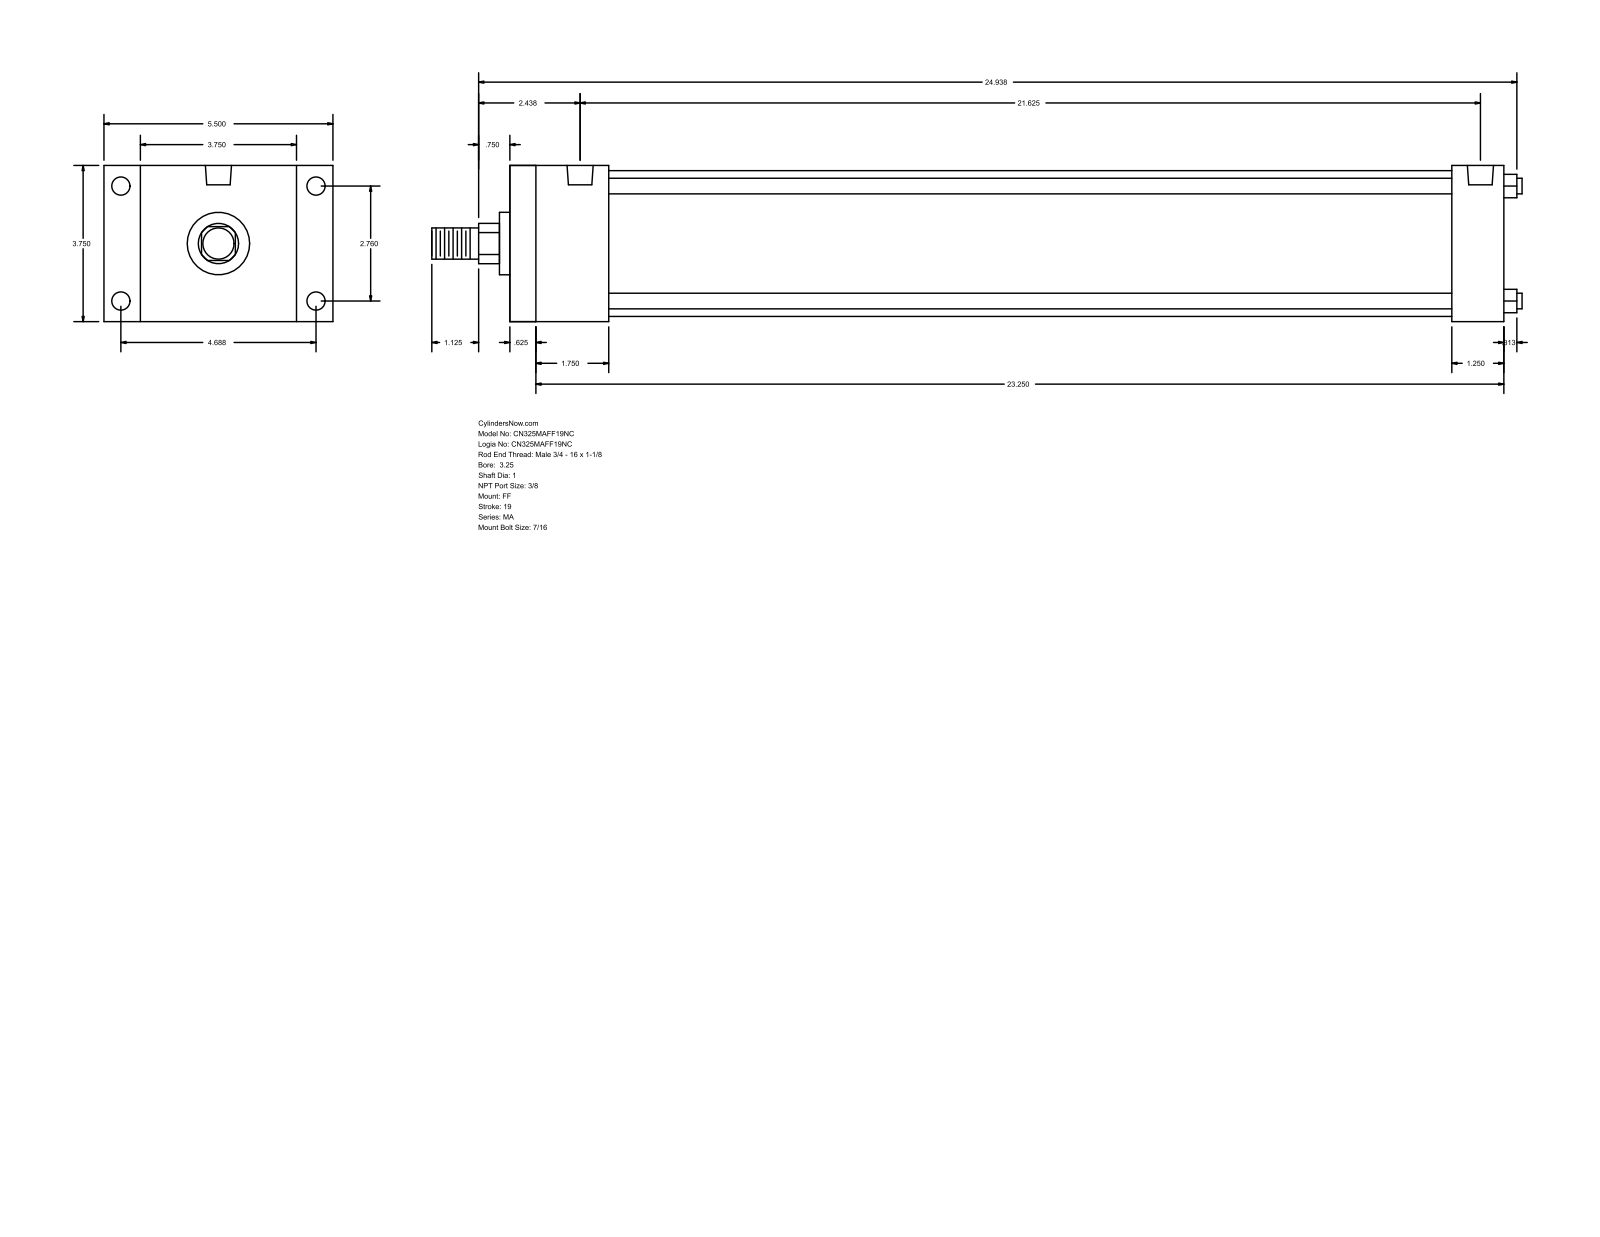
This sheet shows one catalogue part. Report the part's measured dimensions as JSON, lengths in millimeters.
{"part_name": "MA_FF__0325_1", "step_written_by": "GSSL Pune (CONFIG_CONTROL_DESIGN)", "units": "millimeters", "bodies": {"solids": 0, "faces": 92, "planar": 64, "cylindrical": 28, "other": 0}, "overall_size": [665.16, 139.7, 95.25], "round_holes": [[11.11, 8], [15.93, 2]], "round_bosses_or_shafts": [[9.53, 4], [88.9, 1], [38.1, 1], [25.4, 1], [19.05, 1]], "partial_cylinders_radius": [[12.29, 1]], "face_to_face_distances": [95.24, 606.43, 15.87, 590.56, 22.23, 117.47, 60.33, 574.68, 44.46, 558.81], "hole_center_spacings": [70.1, 119.06, 138.16, 539.75, 4.76, 4.77, 544.51, 544.52]}
